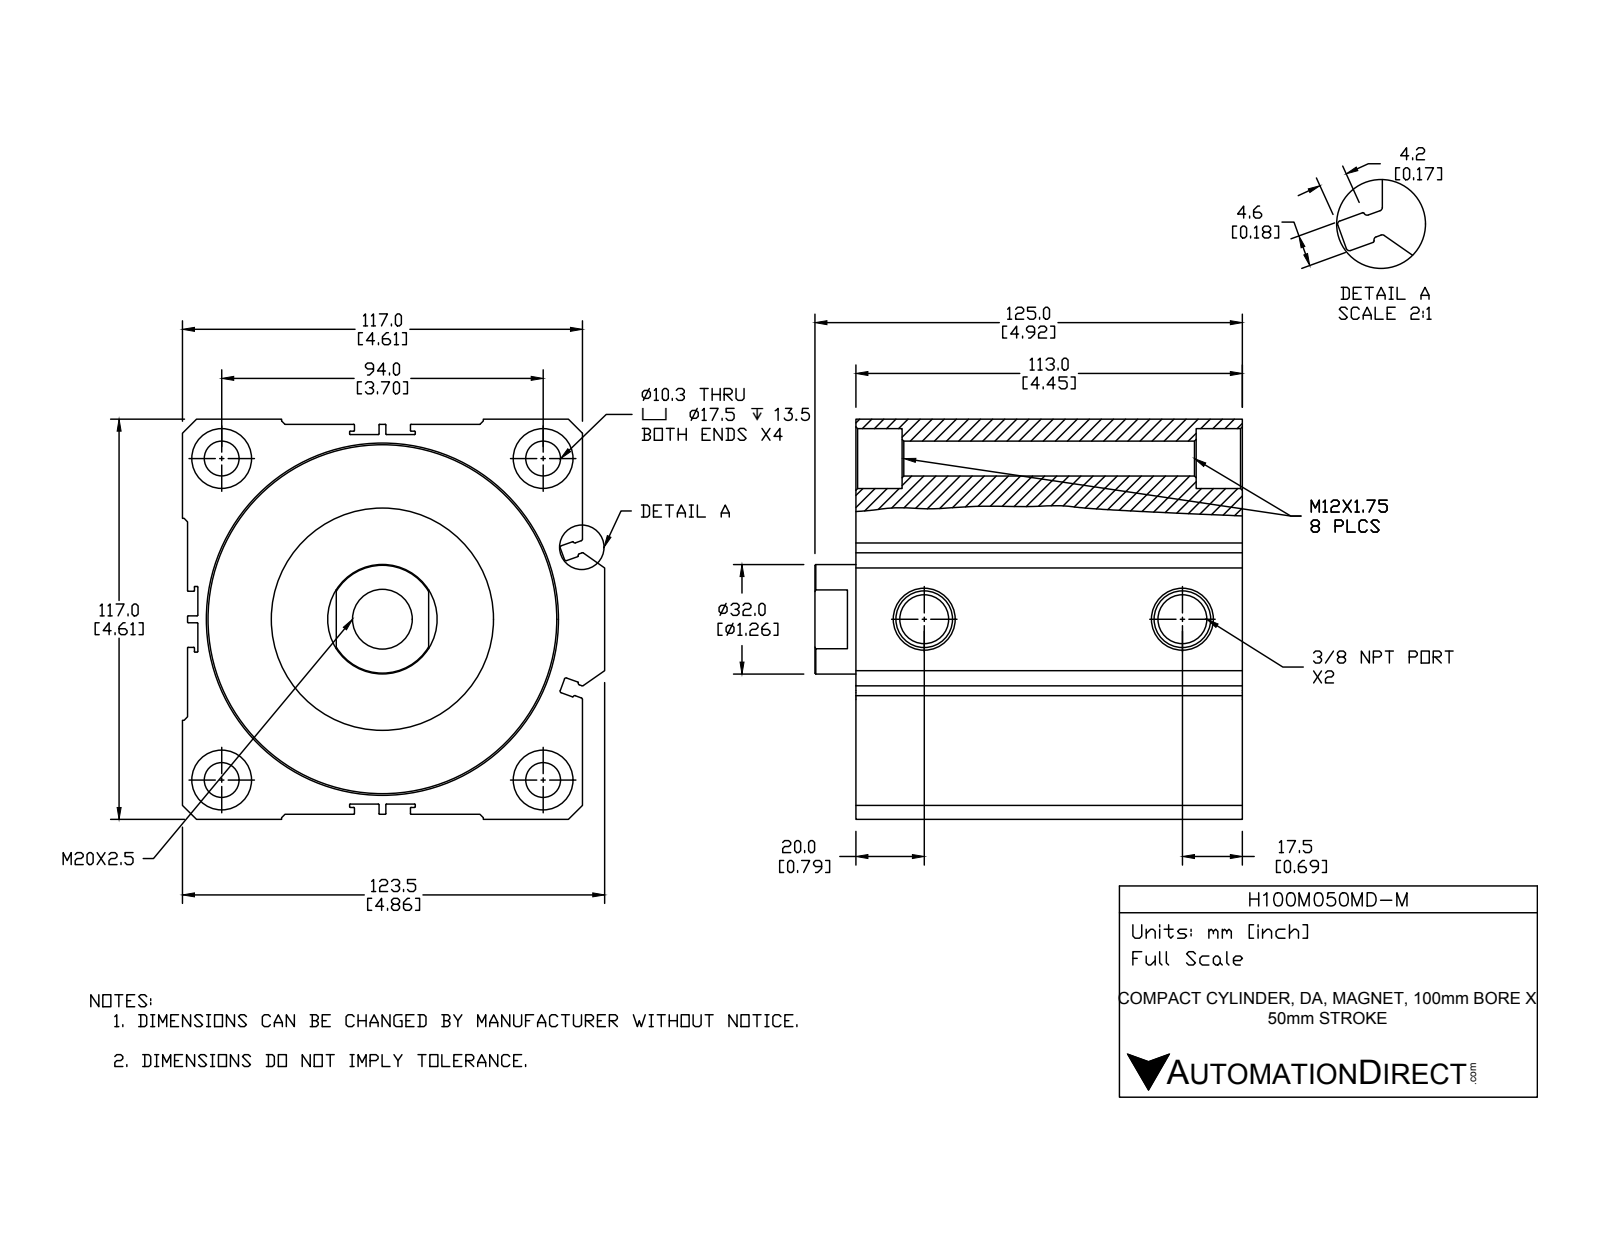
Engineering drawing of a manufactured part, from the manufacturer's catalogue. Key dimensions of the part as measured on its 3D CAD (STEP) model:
Part name (STEP PRODUCT): H100M050MD-M-PISTON; H100M050MD-M; H100M050MD-M-BODY
STEP written by: SolidWorks 2015 (CONFIG_CONTROL_DESIGN)
Units: millimetres
Bodies: 2 solids, 261 faces (105 planar, 103 cylindrical, 53 other)
Overall size (bounding box): 125 × 123.5 × 117
Volume: 1 039 000 mm³ · Surface area: 186 852 mm²
Round holes (diameter × count): ⌀17.5 ×5, ⌀10.2 ×4, ⌀14.27 ×2, ⌀32 ×1, ⌀65 ×1, ⌀100 ×1, ⌀102 ×1
Round bosses / shafts (diameter × count): ⌀39 ×1
Partial cylindrical surfaces — rounded edges, fillets, slot ends (radius × count): R0.2 ×40, R0.5 ×12
Main face-to-face distances: 115.5, 1.5, 117, 111, 27.8, 78.5, 50.7, 12.5, 40.3, 91
Hole centre spacings: 66.47, 94, 132.94, 75.5
